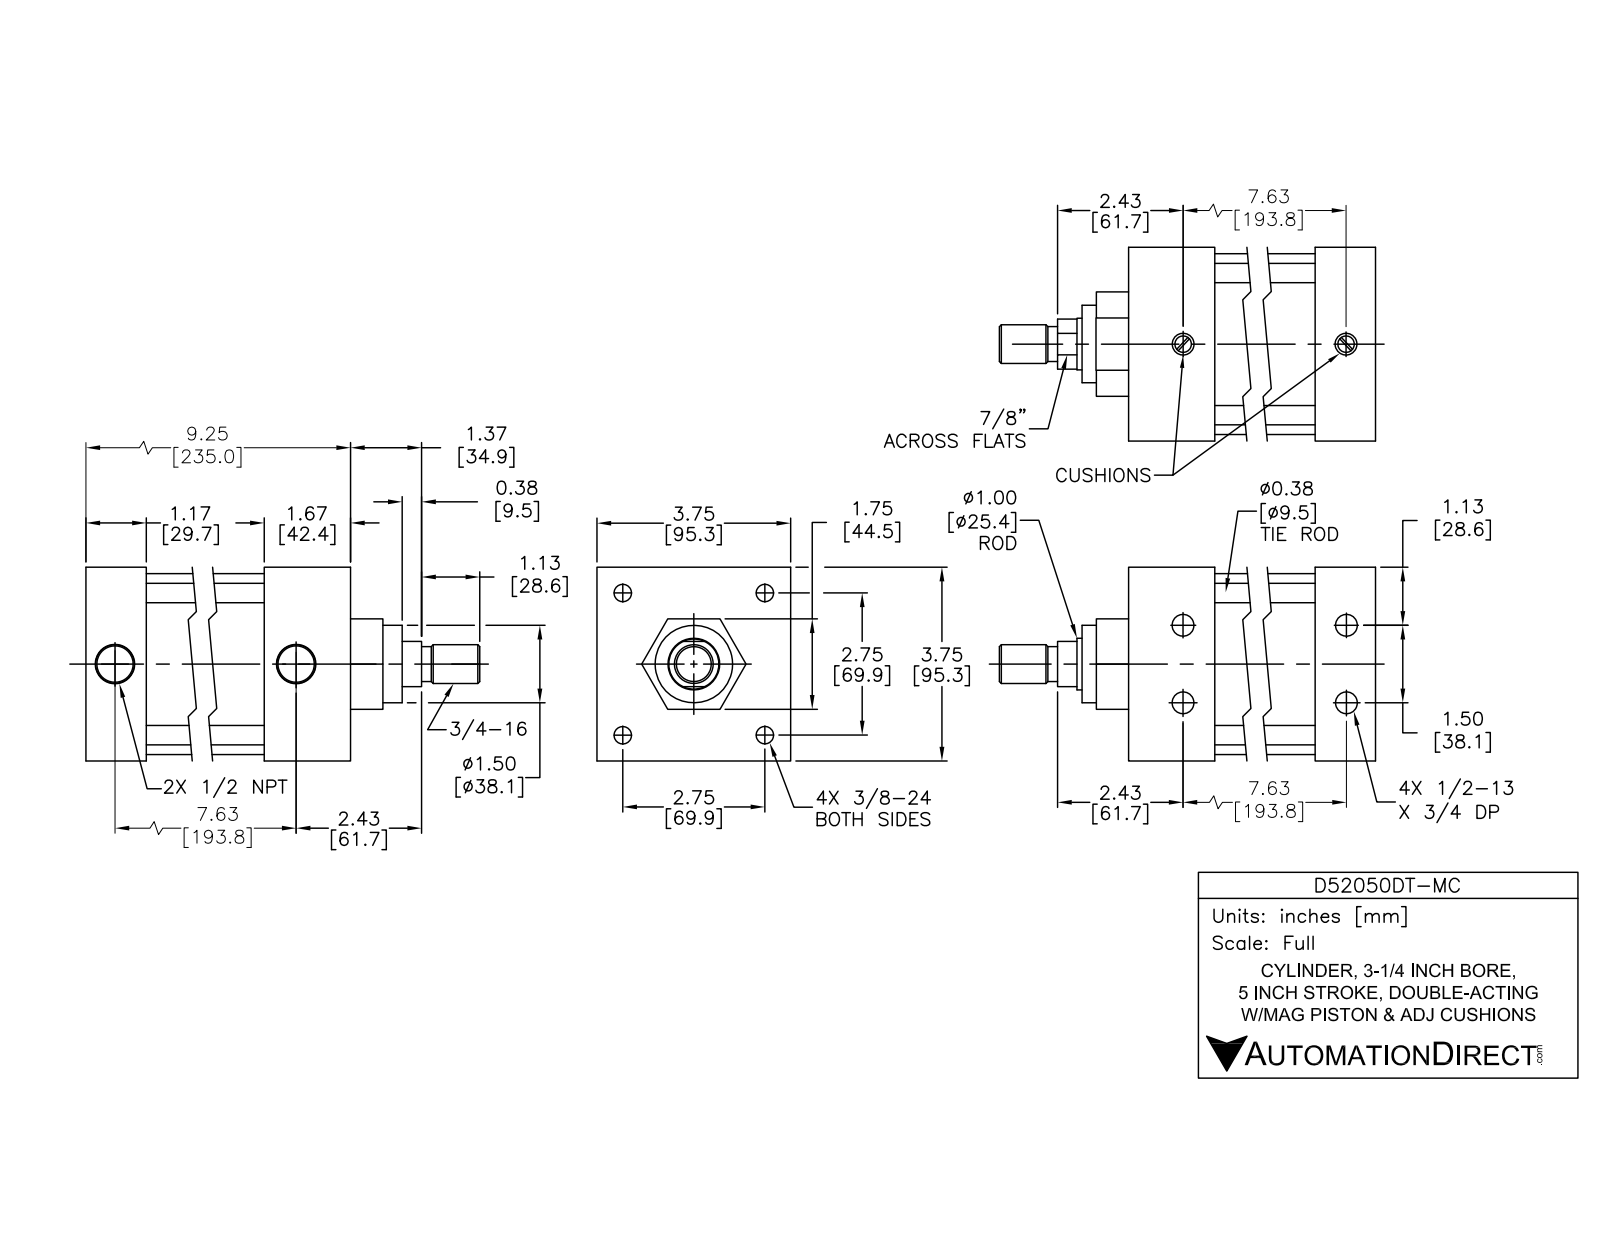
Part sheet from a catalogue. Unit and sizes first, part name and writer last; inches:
Units: inches
Overall size (bounding box): 11.745 × 3.75 × 3.75
Round holes (diameter × count): ⌀0.33 ×4, ⌀0.406 ×4, ⌀0.417 ×4, ⌀0.625 ×4, ⌀0.5 ×2, ⌀0.766 ×2, ⌀1 ×1, ⌀1.003 ×1, ⌀3.25 ×1
Round bosses / shafts (diameter × count): ⌀0.609 ×4, ⌀0.375 ×4, ⌀0.34 ×4, ⌀3.5 ×1, ⌀3.247 ×1, ⌀1.75 ×1, ⌀0.997 ×1, ⌀0.97 ×1
Partial cylindrical surfaces — rounded edges, fillets, slot ends (radius × count): R0.375 ×4
Main face-to-face distances: 3.75, 0.08, 6.326, 9.246, 1.75, 7.997, 1.249, 6.751, 1.246, 2.495
Hole centre spacings: 0.75, 0.76, 1.5, 1.95, 1.95, 2.758, 2.758, 3.9
Volume: 66.17 in³ · Surface area: 380.1 in²
Bodies: 12 solids, 303 faces (99 planar, 114 cylindrical, 90 other)
Part name (STEP PRODUCT): D52050DT-M BODY; D52050DT-MC; D52050DT-M PISTON
STEP written by: SolidWorks 2015 (AUTOMOTIVE_DESIGN)
